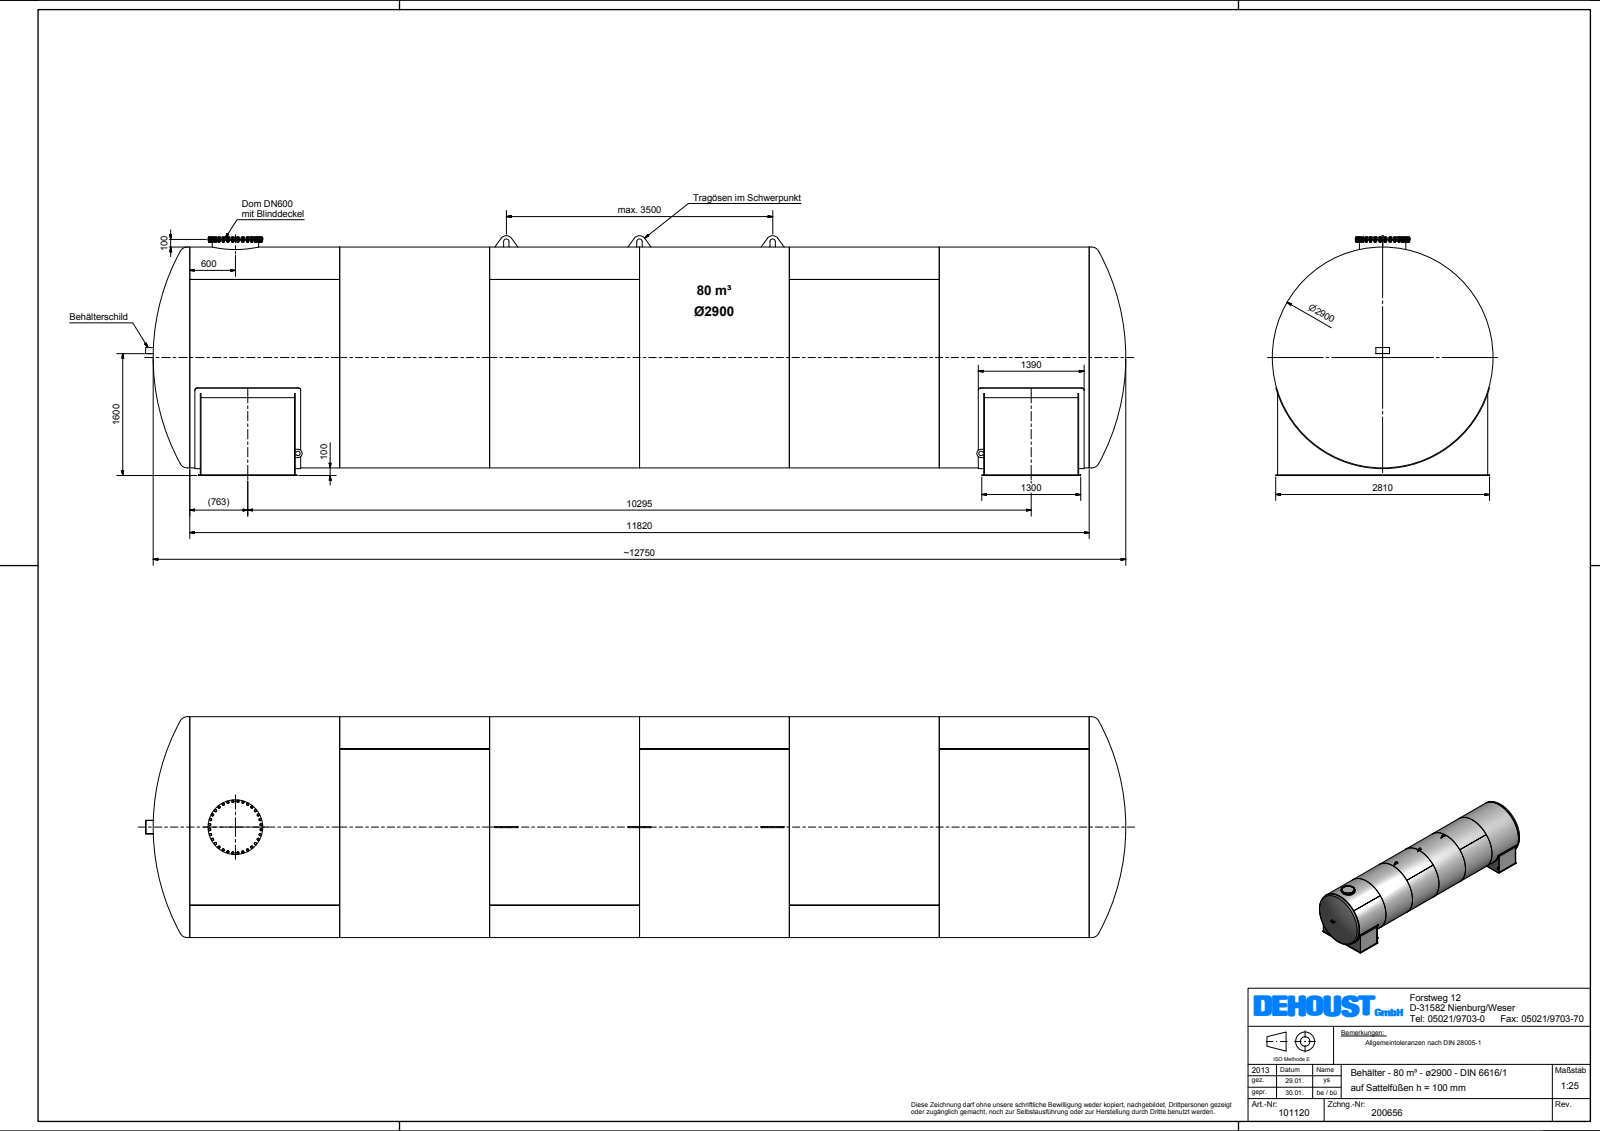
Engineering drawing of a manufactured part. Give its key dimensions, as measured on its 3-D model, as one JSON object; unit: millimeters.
{"part_name": "Beh\\S\\dlter_6616_E_2900_080_100_KV", "step_written_by": "Autodesk Inventor 2012 (AUTOMOTIVE_DESIGN)", "units": "millimeters", "bodies": {"solids": 5, "faces": 1157, "planar": 690, "cylindrical": 175, "other": 292}, "overall_size": [12880.62, 3150, 2900], "volume_mm3": 5062000000, "surface_area_mm2": 277500000, "round_holes": [[598, 1], [2882, 1]], "round_bosses_or_shafts": [[24.8, 32], [18, 32], [16.65, 32], [2900, 1], [720, 1], [660, 1], [610, 1]], "partial_cylinders_radius": [[30, 8], [35, 3], [85, 3], [29.73, 2], [55, 2], [1459, 1]], "face_to_face_distances": [9, 11820, 2711, 10295, 1239, 2720, 2702, 138.5, 11681.5, 1386.5]}
